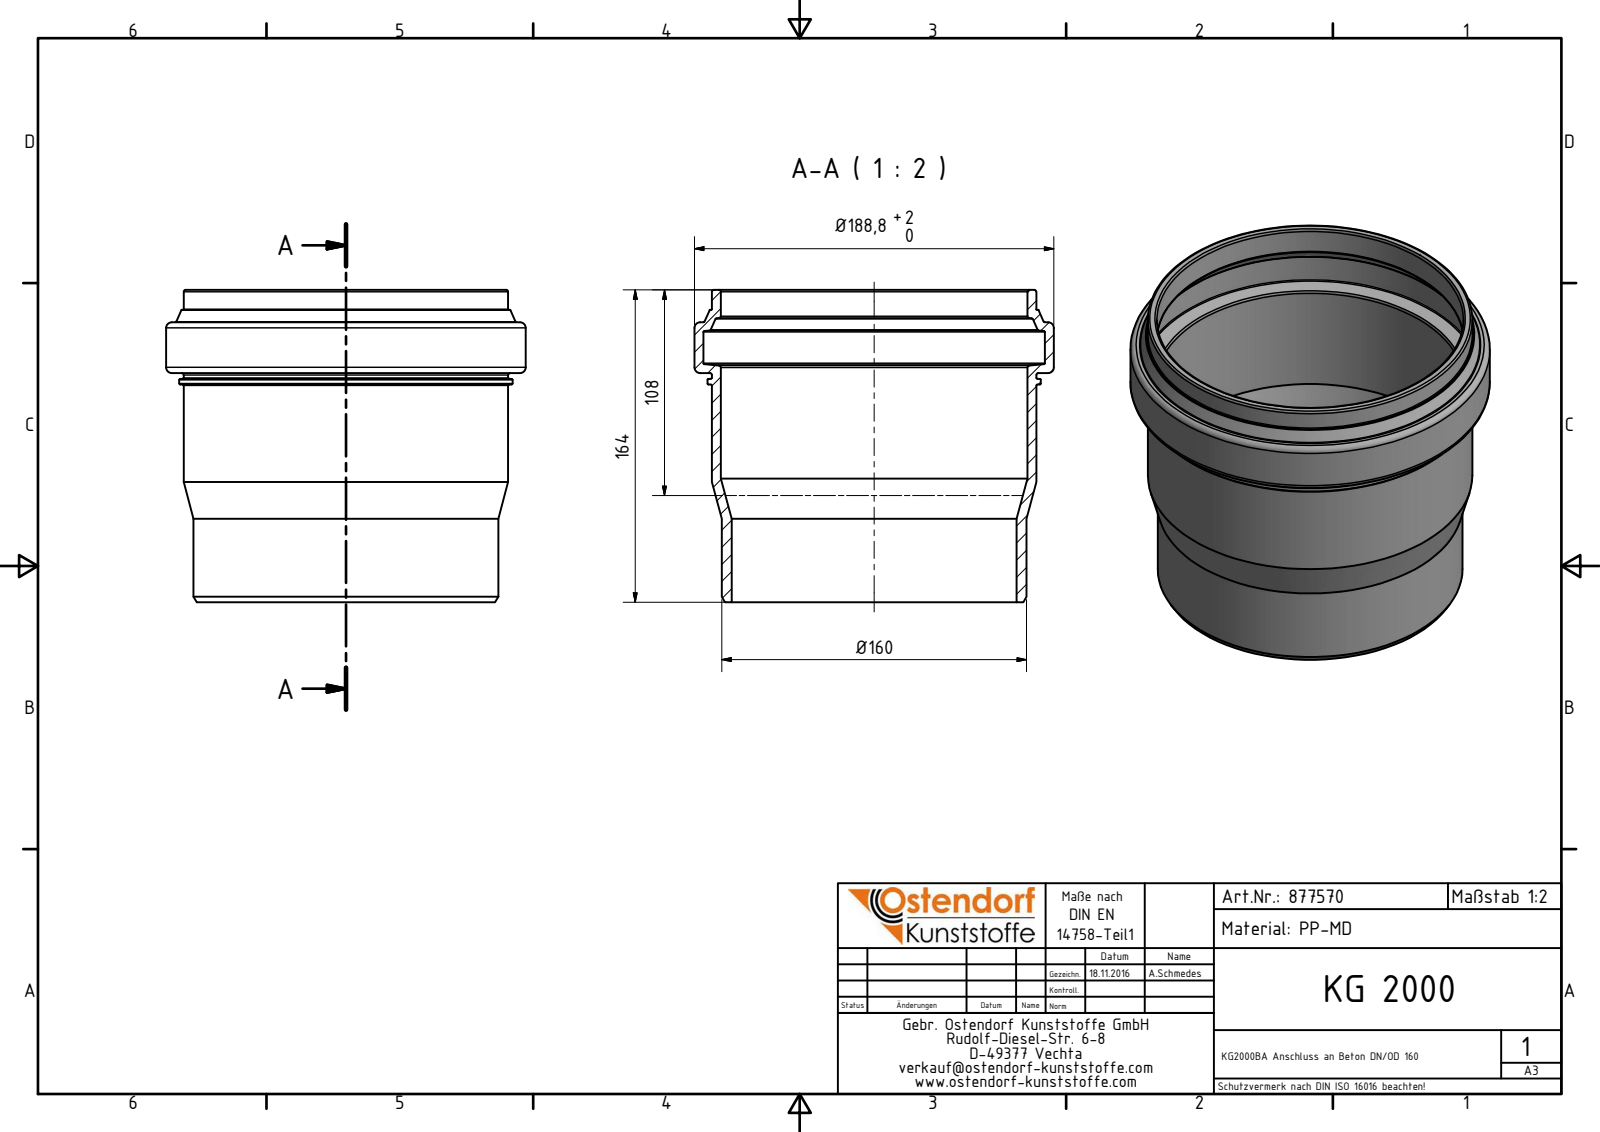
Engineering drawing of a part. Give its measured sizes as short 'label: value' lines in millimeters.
name: 877570 KG2000BA Anschluss an Beton DN_OD 160
written by: Autodesk Inventor 2016 (AUTOMOTIVE_DESIGN)
unit: mm
bodies: 1 solid, 43 faces (7 planar, 10 cylindrical, 26 other)
size: 188.8 × 188.8 × 164
volume: 453 795 mm³; area: 191 105 mm²
holes: 1× ⌀149.7, 1× ⌀161, 1× ⌀179.4
bosses: 1× ⌀188.8, 1× ⌀175.1, 1× ⌀170.4, 1× ⌀160.1
face distances: 120.3, 3, 164, 43.7, 147, 26.7, 17, 117.3, 29.7, 46.7
